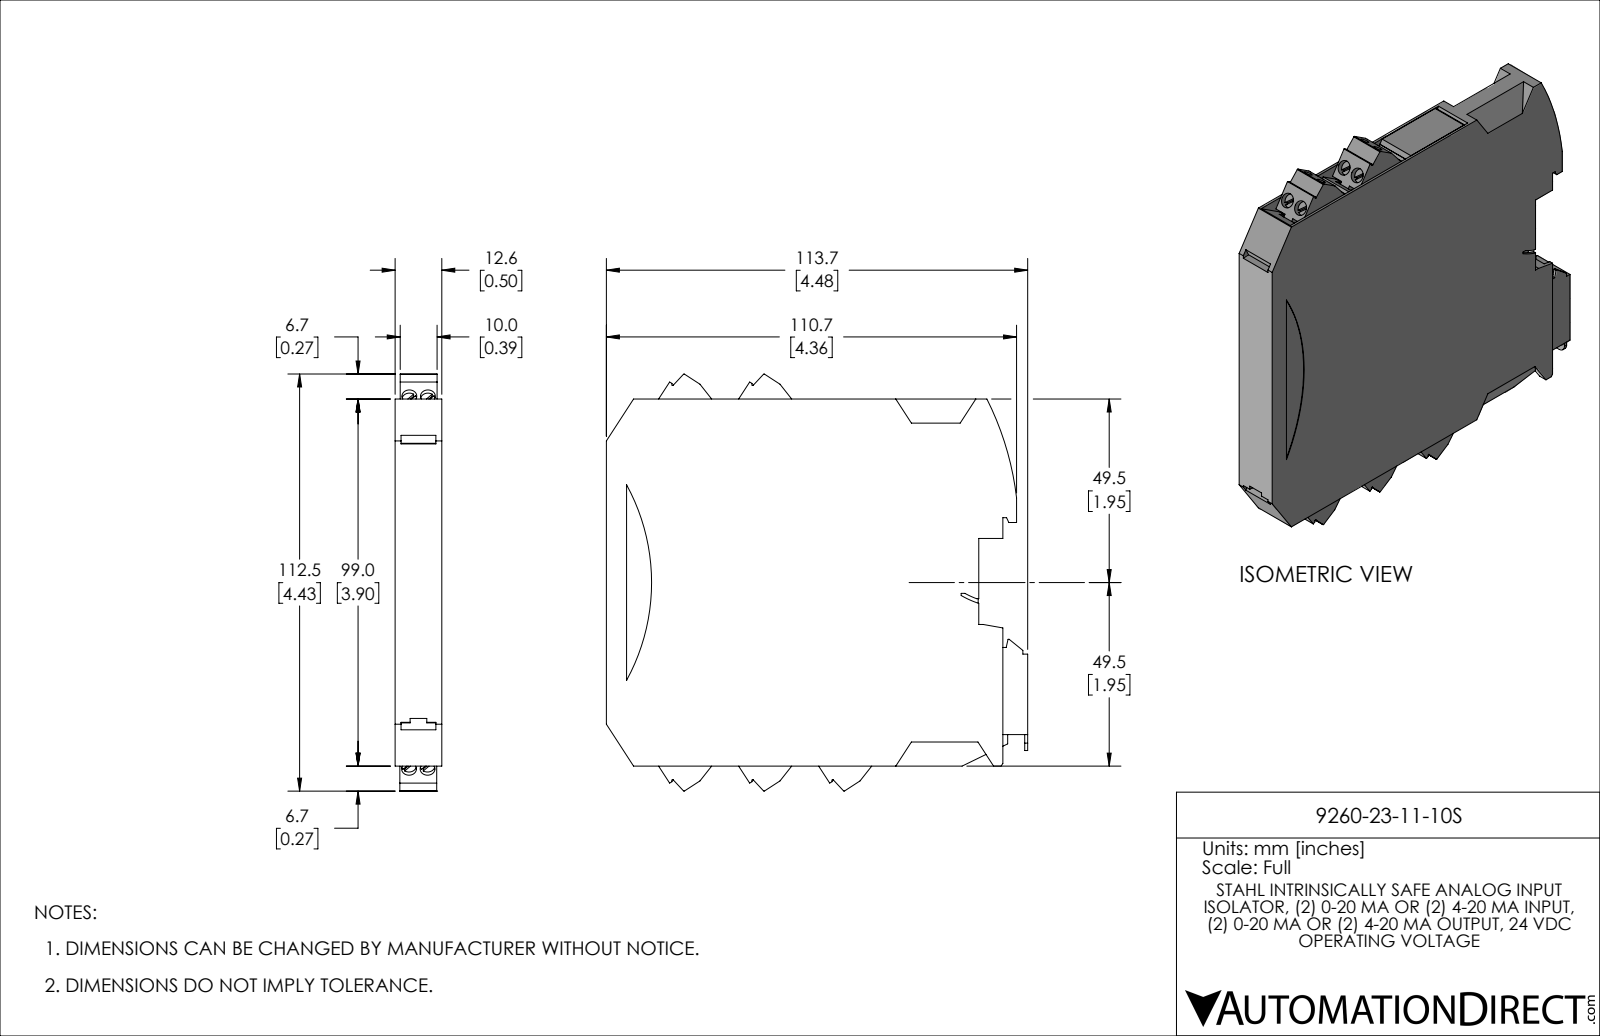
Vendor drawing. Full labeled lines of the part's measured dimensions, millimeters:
Part name (STEP PRODUCT): 9260-23-11-10s
STEP written by: SolidWorks 2019 (AUTOMOTIVE_DESIGN)
Units: millimetres
Bodies: 7 solids, 956 faces (854 planar, 92 cylindrical, 10 other)
Overall size (bounding box): 113.7 × 112.5 × 12.6
Volume: 127 100 mm³ · Surface area: 41 660 mm²
Round holes (diameter × count): ⌀1.5 ×10, ⌀2.2 ×10, ⌀3 ×10, ⌀4 ×10
Round bosses / shafts (diameter × count): ⌀2.8 ×6
Partial cylindrical surfaces — rounded edges, fillets, slot ends (radius × count): R3 ×13, R2.9 ×10, R1.4 ×6, R0.2 ×5, R2 ×2, R0.5 ×1, R1.5 ×1, R2.5 ×1
Main face-to-face distances: 12.6, 0.8, 11.9, 18.1, 10, 1.3, 11.3, 0.5, 10.6, 1.4
Hole centre spacings: 5, 18.1, 18.8, 21.6, 22.1, 11.8, 12.8, 11.8
